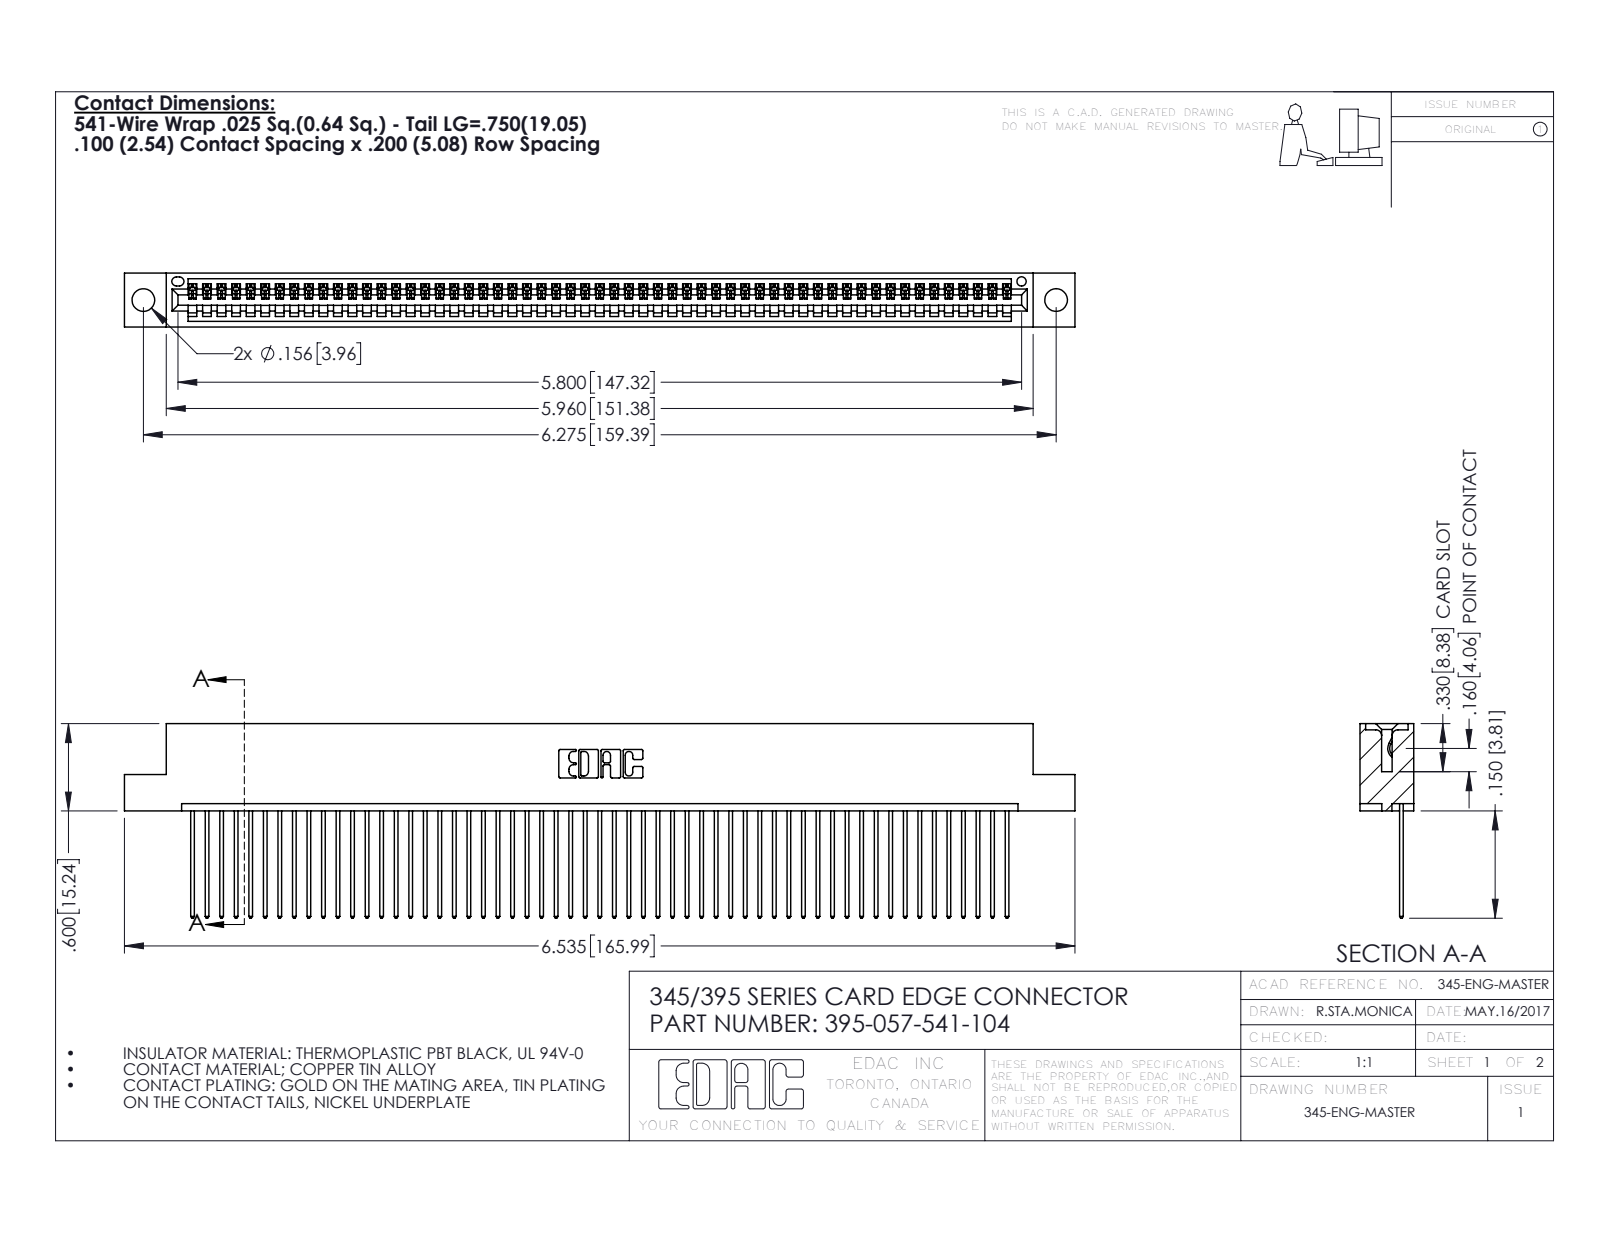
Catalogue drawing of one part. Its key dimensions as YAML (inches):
part_name: "395-057-541-104; 345-292-001_345-293-141; 345 Part_Flush Mounting Lugs - 0.156 Dia-TH"
step_written_by: "SolidWorks 2016 (CONFIG_CONTROL_DESIGN)"
units: inches
bodies: {solids: 58, faces: 3432, planar: 2360, cylindrical: 1072, other: 0}
overall_size: [6.535, 1.337, 0.37]
volume: 0.976
surface_area: 34.67
round_holes:
  - {diameter: 0.156, count: 2}
  - {diameter: 0.064, count: 1}
partial_cylinders:
  - {radius: 0.006, count: 114}
  - {radius: 0.01, count: 114}
  - {radius: 0.01, count: 22}
  - {radius: 0.007, count: 6}
  - {radius: 0.031, count: 6}
  - {radius: 0.026, count: 3}
  - {radius: 0.031, count: 2}
  - {radius: 0.04, count: 2}
face_to_face_distances: [0.072, 0.298, 0.098, 0.272, 0.025, 0.37, 0.2, 0.225, 0.149, 0.072]
hole_center_spacings: [0.27, 6.039, 6.275]
